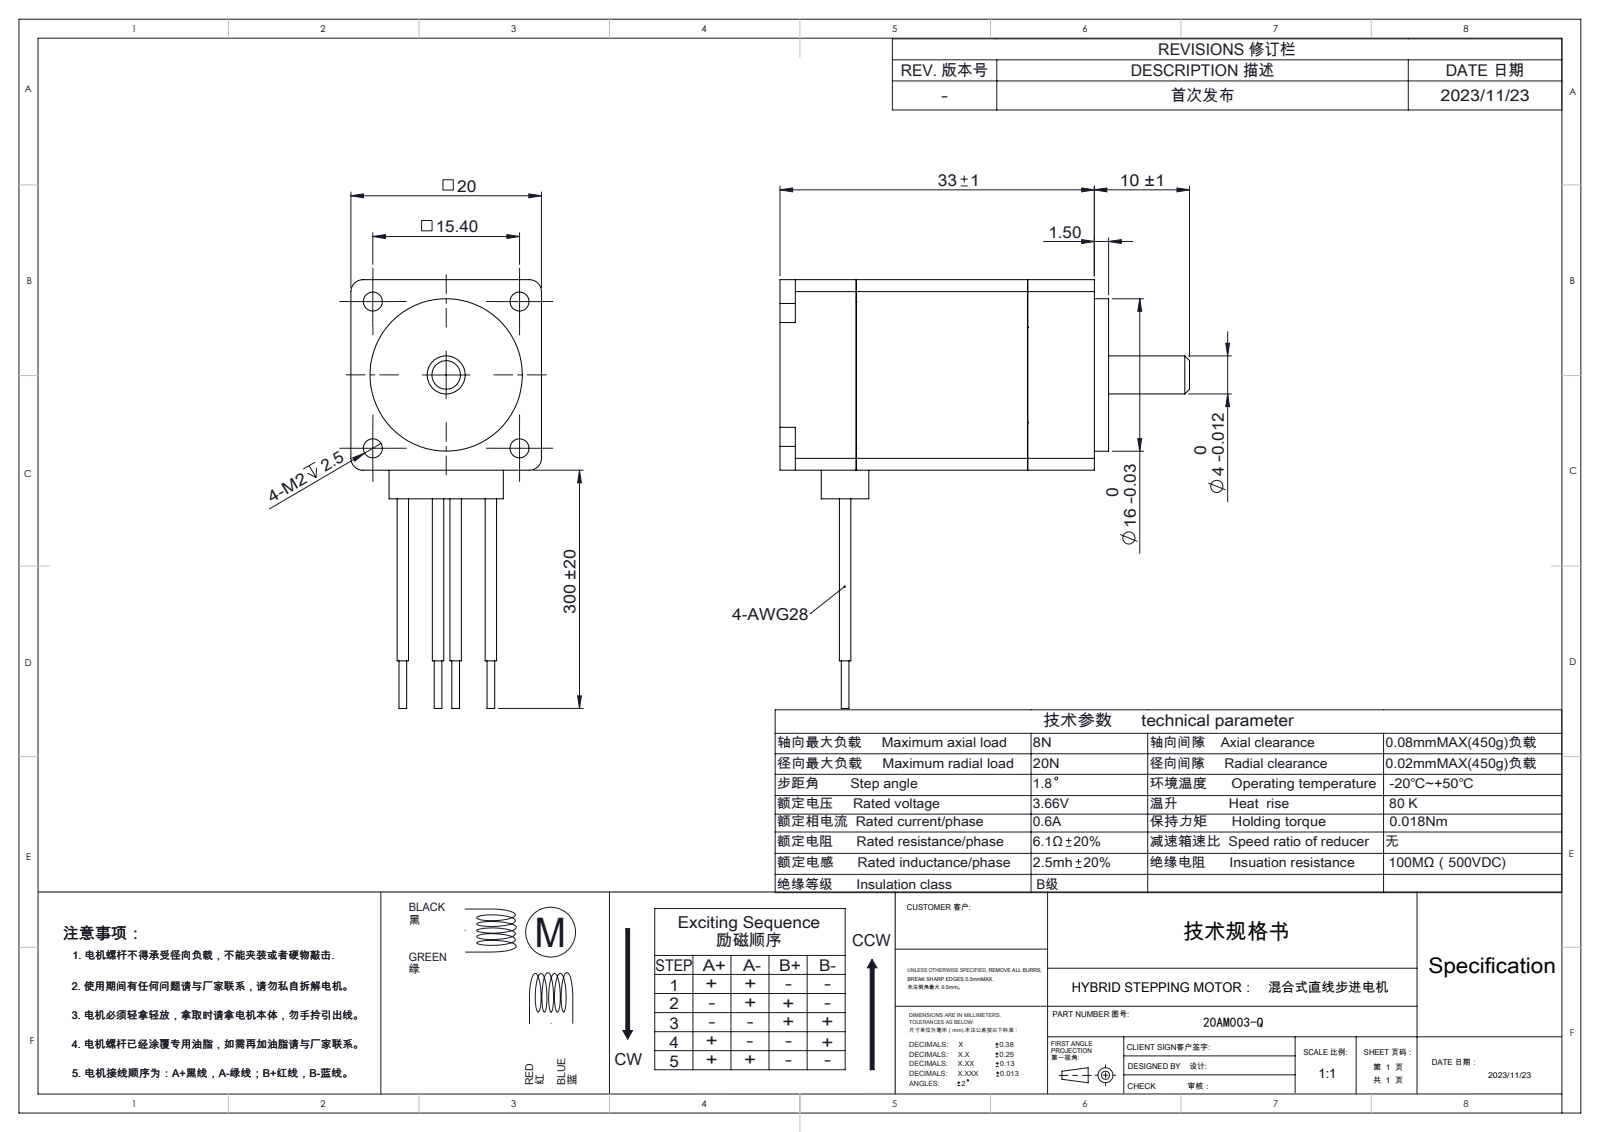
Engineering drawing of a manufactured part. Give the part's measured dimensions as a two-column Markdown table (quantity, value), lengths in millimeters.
| quantity | value |
| --- | --- |
| part name | 20HS233-0604-002 |
| STEP written by | SolidWorks 2020 (AUTOMOTIVE_DESIGN) |
| units | millimeters |
| bodies | 2 solids, 115 faces (47 planar, 64 cylindrical, 4 other) |
| overall size | 45 × 43 × 20 |
| volume | 13 330 mm³ |
| surface area | 5 772 mm² |
| round holes (diameter × count) | 2 × 4 |
| round bosses / shafts (diameter × count) | 1.2 × 4, 0.8 × 4, 16 × 1, 15.35 × 1, 10.02 × 1, 4 × 1 |
| partial cylindrical surfaces (radius × count) | 1.25 × 4, 2 × 4 |
| main face-to-face distances | 20, 18, 8, 26, 8.5, 34.5, 26.5, 25, 33, 7 |
| hole center spacings | 15.4, 21.78 |
